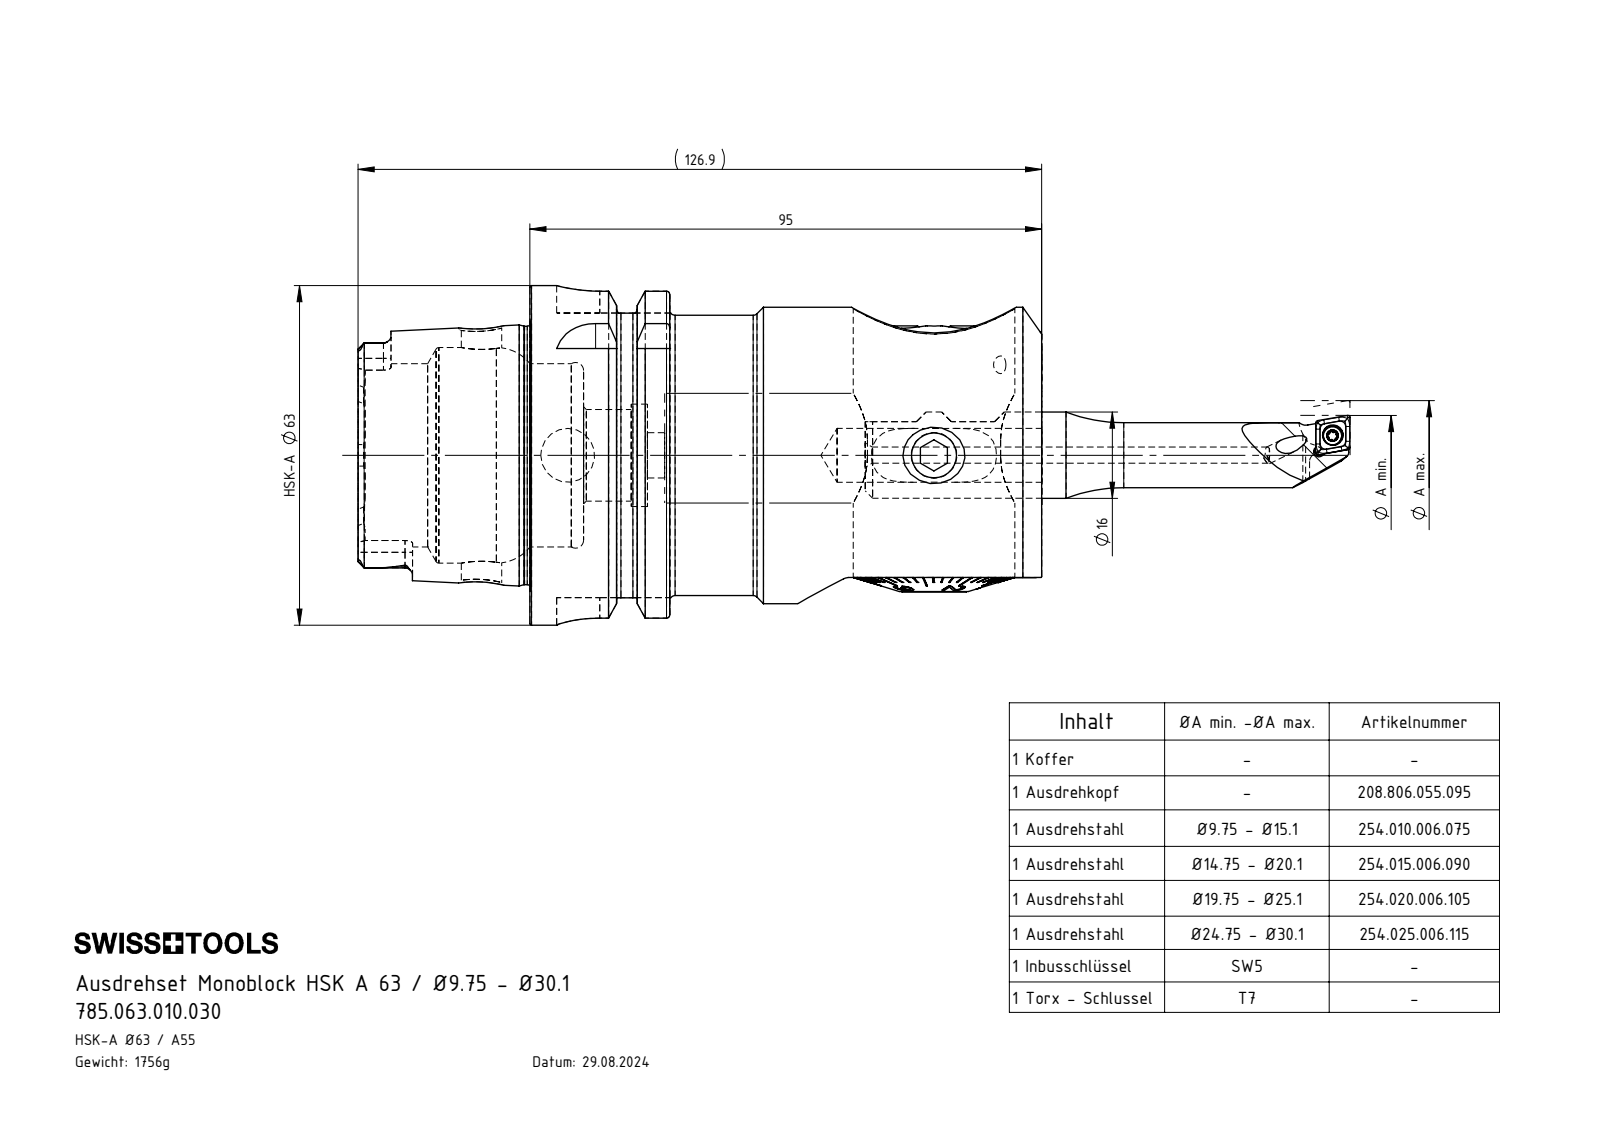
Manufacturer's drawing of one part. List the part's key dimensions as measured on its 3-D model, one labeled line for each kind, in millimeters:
Part name (STEP PRODUCT): A55-BG3.011.033_A_gekürzt; A55-BG2.012.006_B; CCMT060204; ISO 4026 - M10 x 16_PreviewCfg (+8 more)
STEP written by: SolidWorks 2022 (AUTOMOTIVE_DESIGN)
Units: millimetres
Bodies: 28 solids, 1422 faces (518 planar, 339 cylindrical, 565 other)
Overall size (bounding box): 238.4 × 126.9 × 63
Volume: 274 659 mm³ · Surface area: 79 657 mm²
Round holes (diameter × count): ⌀3 ×8, ⌀2.05 ×4, ⌀2.8 ×4, ⌀3.85 ×4, ⌀2 ×3, ⌀8.5 ×3, ⌀10 ×2, ⌀1.6 ×1, ⌀2.1 ×1, ⌀3.3 ×1, ⌀4.2 ×1, ⌀7.5 ×1
Round bosses / shafts (diameter × count): ⌀16 ×4, ⌀3.4 ×4, ⌀2.5 ×4, ⌀10 ×3, ⌀18 ×2, ⌀63 ×1, ⌀55 ×1, ⌀54.95 ×1
Partial cylindrical surfaces — rounded edges, fillets, slot ends (radius × count): R0.21 ×24, R0.36 ×17, R1.4 ×10, R0.36 ×7, R0.34 ×6, R0.59 ×6, R8 ×6, R0.5 ×4
Main face-to-face distances: 95, 31.9, 126.9, 16, 57.85, 25.95, 69.05, 41.85, 9.95, 85.05
Hole centre spacings: 14.5, 3.89, 3.99, 7.25, 42.76, 0.33, 3.88, 3.98
